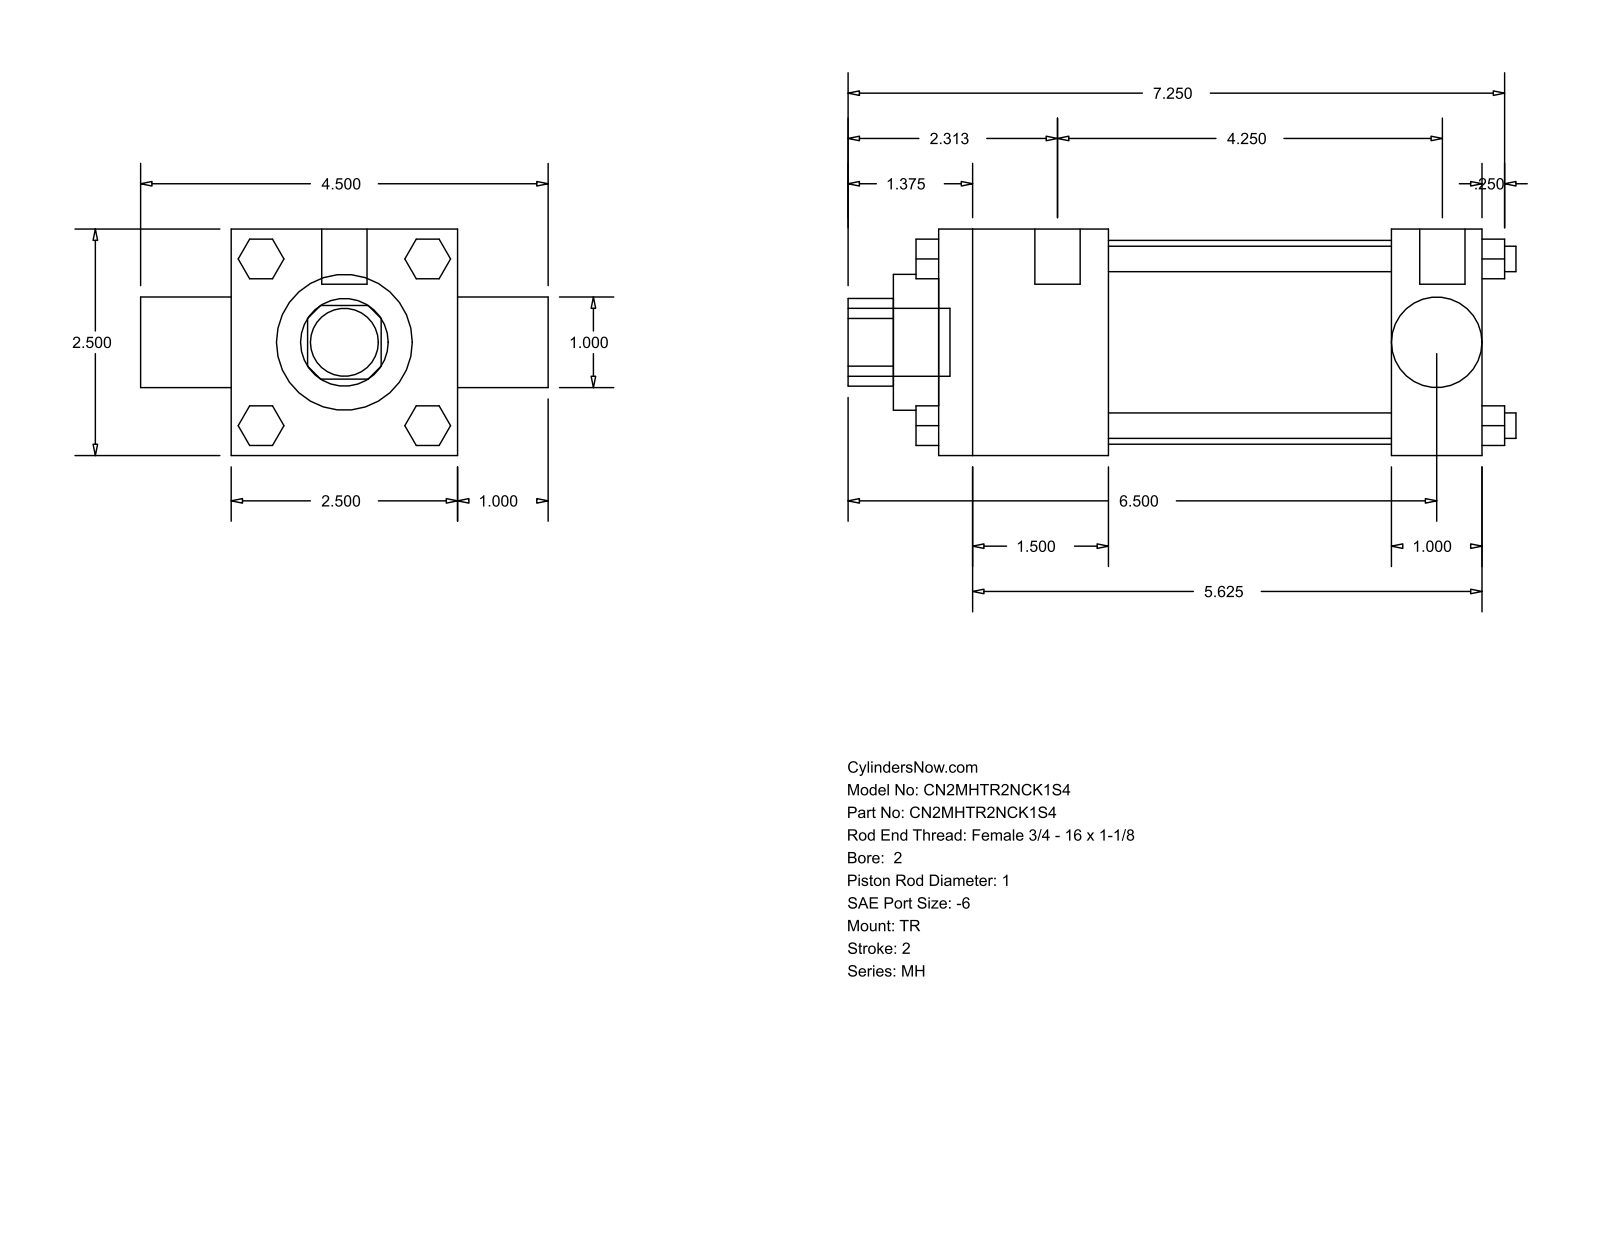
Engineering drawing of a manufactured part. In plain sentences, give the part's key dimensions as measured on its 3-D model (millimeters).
The part is named "MH_TR__0200_1". Its 3-D file was written by "GSSL Pune (CONFIG_CONTROL_DESIGN)". It is 0 solids with 120 faces: 92 planar, 28 cylindrical and 0 other. Overall it measures 187.32 by 114.3 by 63.5 millimeters. Round holes: 1 of diameter 25.35, 1 of diameter 25.4, 1 of diameter 38.1, 1 of diameter 57.15. Round bosses or shafts: 4 of diameter 7.14, 3 of diameter 5.56, 2 of diameter 12.7, 1 of diameter 19.05. Partial cylindrical surfaces (rounded edges, fillets, slot ends): 1 of radius 12.29. The main face-to-face distances are 63.5, 152.4, 25.4, 47.63, 127, 79.37, 104.77, 88.9, 165.1, 6.35.
